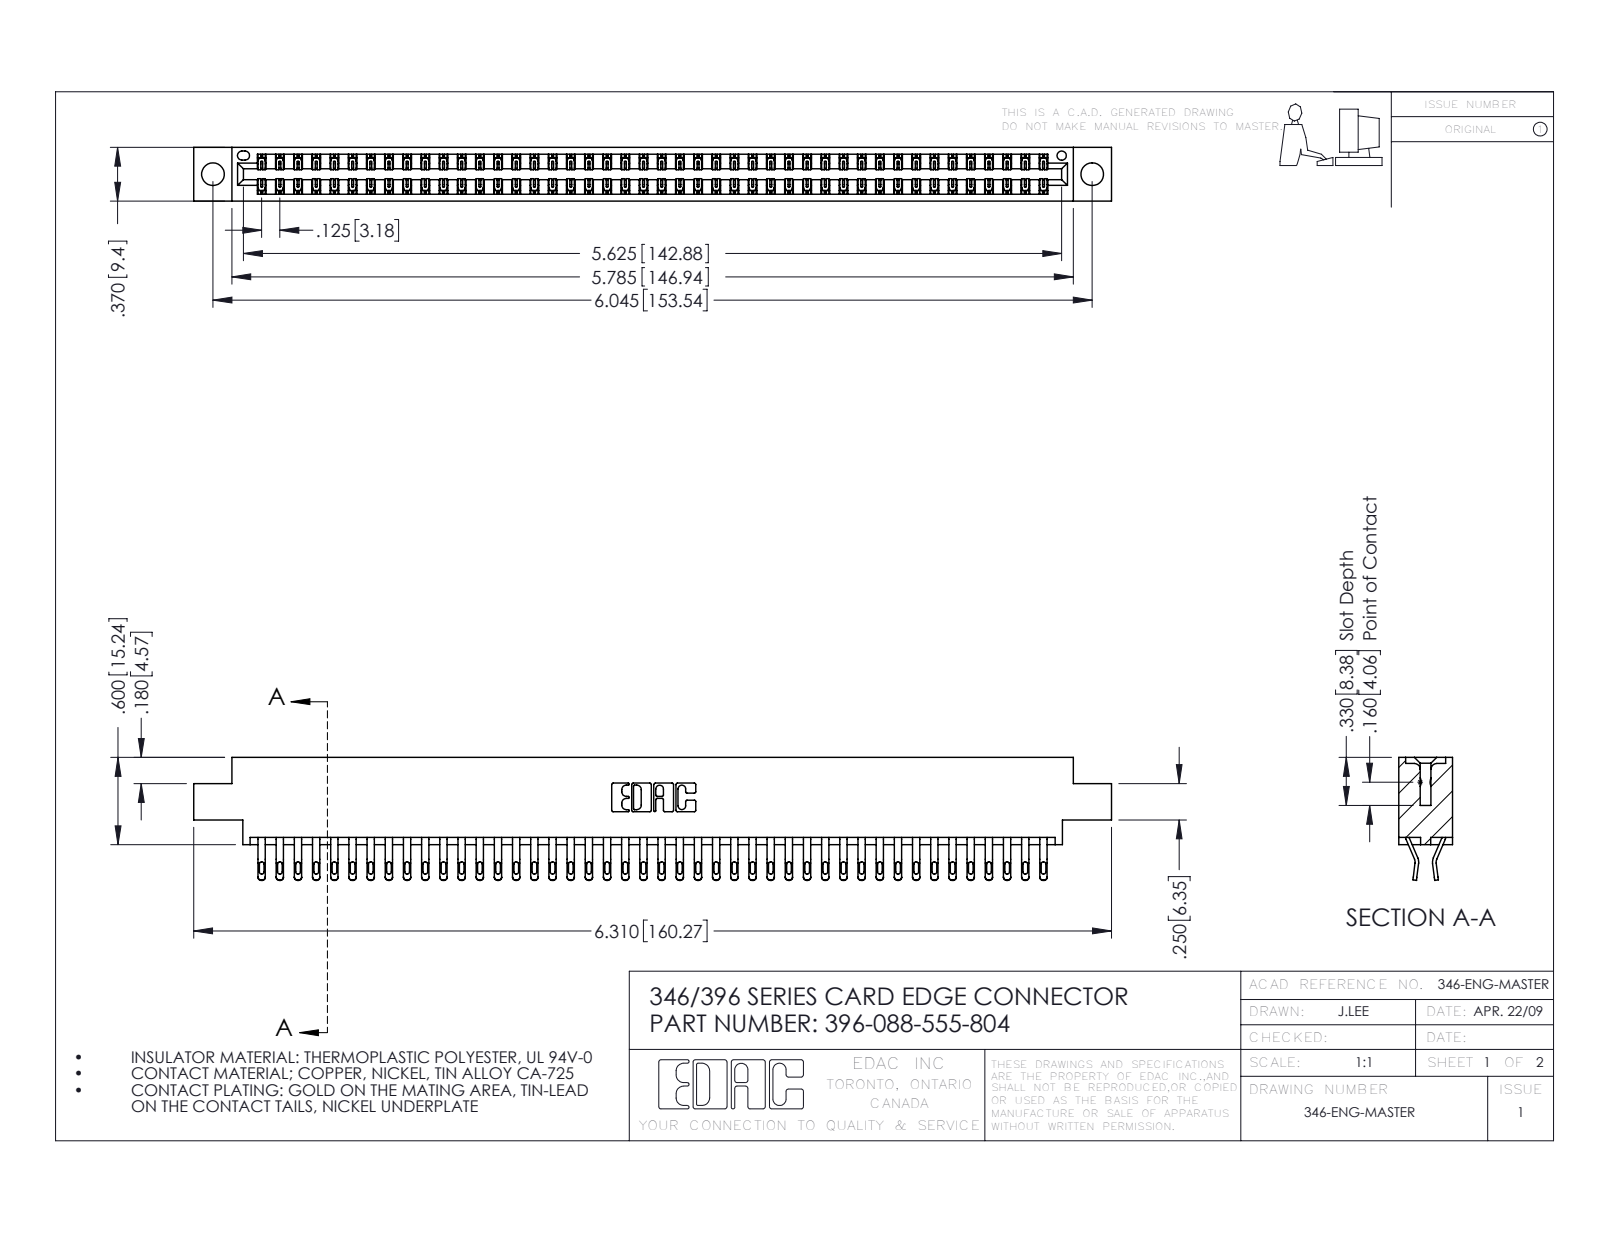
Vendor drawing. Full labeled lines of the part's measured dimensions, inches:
Part name (STEP PRODUCT): 396-088-555-804; 345-292-001_555 Tail; 346 Part_0.170 Offset - 0.156 Dia-TH
STEP written by: SolidWorks 2016 (CONFIG_CONTROL_DESIGN)
Units: inches
Bodies: 89 solids, 5230 faces (2984 planar, 2246 cylindrical, 0 other)
Overall size (bounding box): 6.31 × 0.845 × 0.37
Volume: 0.955 in³ · Surface area: 34.81 in²
Round holes (diameter × count): ⌀0.156 ×2, ⌀0.064 ×1
Partial cylindrical surfaces — rounded edges, fillets, slot ends (radius × count): R0.016 ×176, R0.02 ×176, R0.006 ×132, R0.01 ×22, R0.007 ×6, R0.031 ×6, R0.026 ×3, R0.01 ×2
Main face-to-face distances: 0.048, 0.322, 0.37, 0.25, 0.025, 0.072, 0.298, 0.275, 0.148, 0.222
Hole centre spacings: 0.246, 5.836, 6.045
